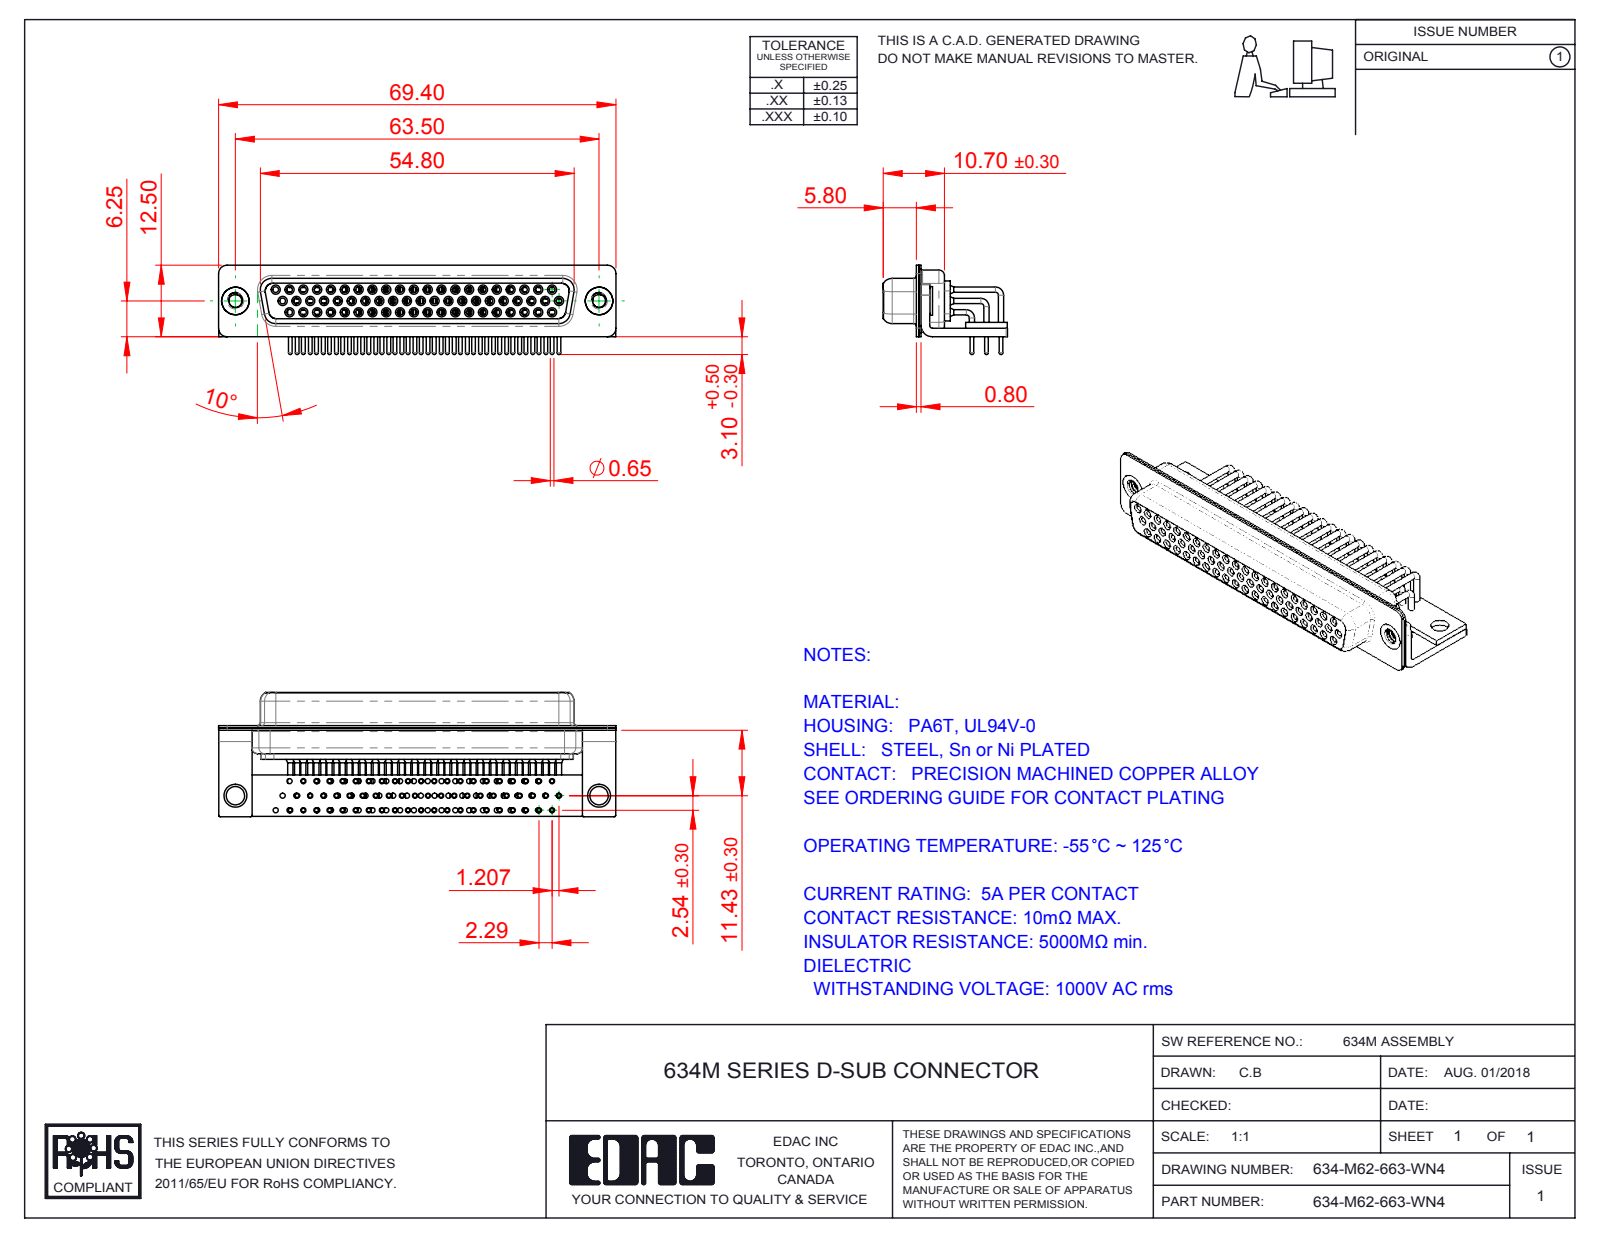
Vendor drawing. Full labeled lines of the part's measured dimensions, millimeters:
Part name (STEP PRODUCT): 634M Shell Rear_62 Contacts; 634-M62-663-WN4; 634M Shell Front_62 Contacts; 634M 4-40 Threaded Rivet_Stabilizer (+6 more)
STEP written by: SolidWorks 2016 (CONFIG_CONTROL_DESIGN)
Units: millimetres
Bodies: 70 solids, 3739 faces (1023 planar, 1709 cylindrical, 1007 other)
Overall size (bounding box): 69.4 × 21.7 × 15.6
Volume: 6 132 mm³ · Surface area: 19 720 mm²
Round holes (diameter × count): ⌀0.9 ×62, ⌀1 ×62, ⌀1.1 ×62, ⌀1.7 ×62, ⌀1.8 ×62, ⌀2 ×62, ⌀2.26 ×2, ⌀3.2 ×2, ⌀4 ×2, ⌀4.8 ×2
Round bosses / shafts (diameter × count): ⌀0.9 ×118, ⌀1.6 ×62, ⌀1.5 ×62, ⌀0.65 ×62, ⌀2 ×56, ⌀5 ×2, ⌀4.9 ×2
Partial cylindrical surfaces — rounded edges, fillets, slot ends (radius × count): R0.25 ×16, R1.5 ×16, R2 ×13, R1.35 ×8, R1.6 ×8, R0.5 ×5, R0.6 ×4, R0.65 ×4
Main face-to-face distances: 0.4, 2.3, 1.9, 1, 1.45, 8.95, 8.5, 0.85, 0.8, 9.35
Hole centre spacings: 7.24, 2.41, 9.65, 4.83, 14.48, 16.89, 2.81, 2.32
